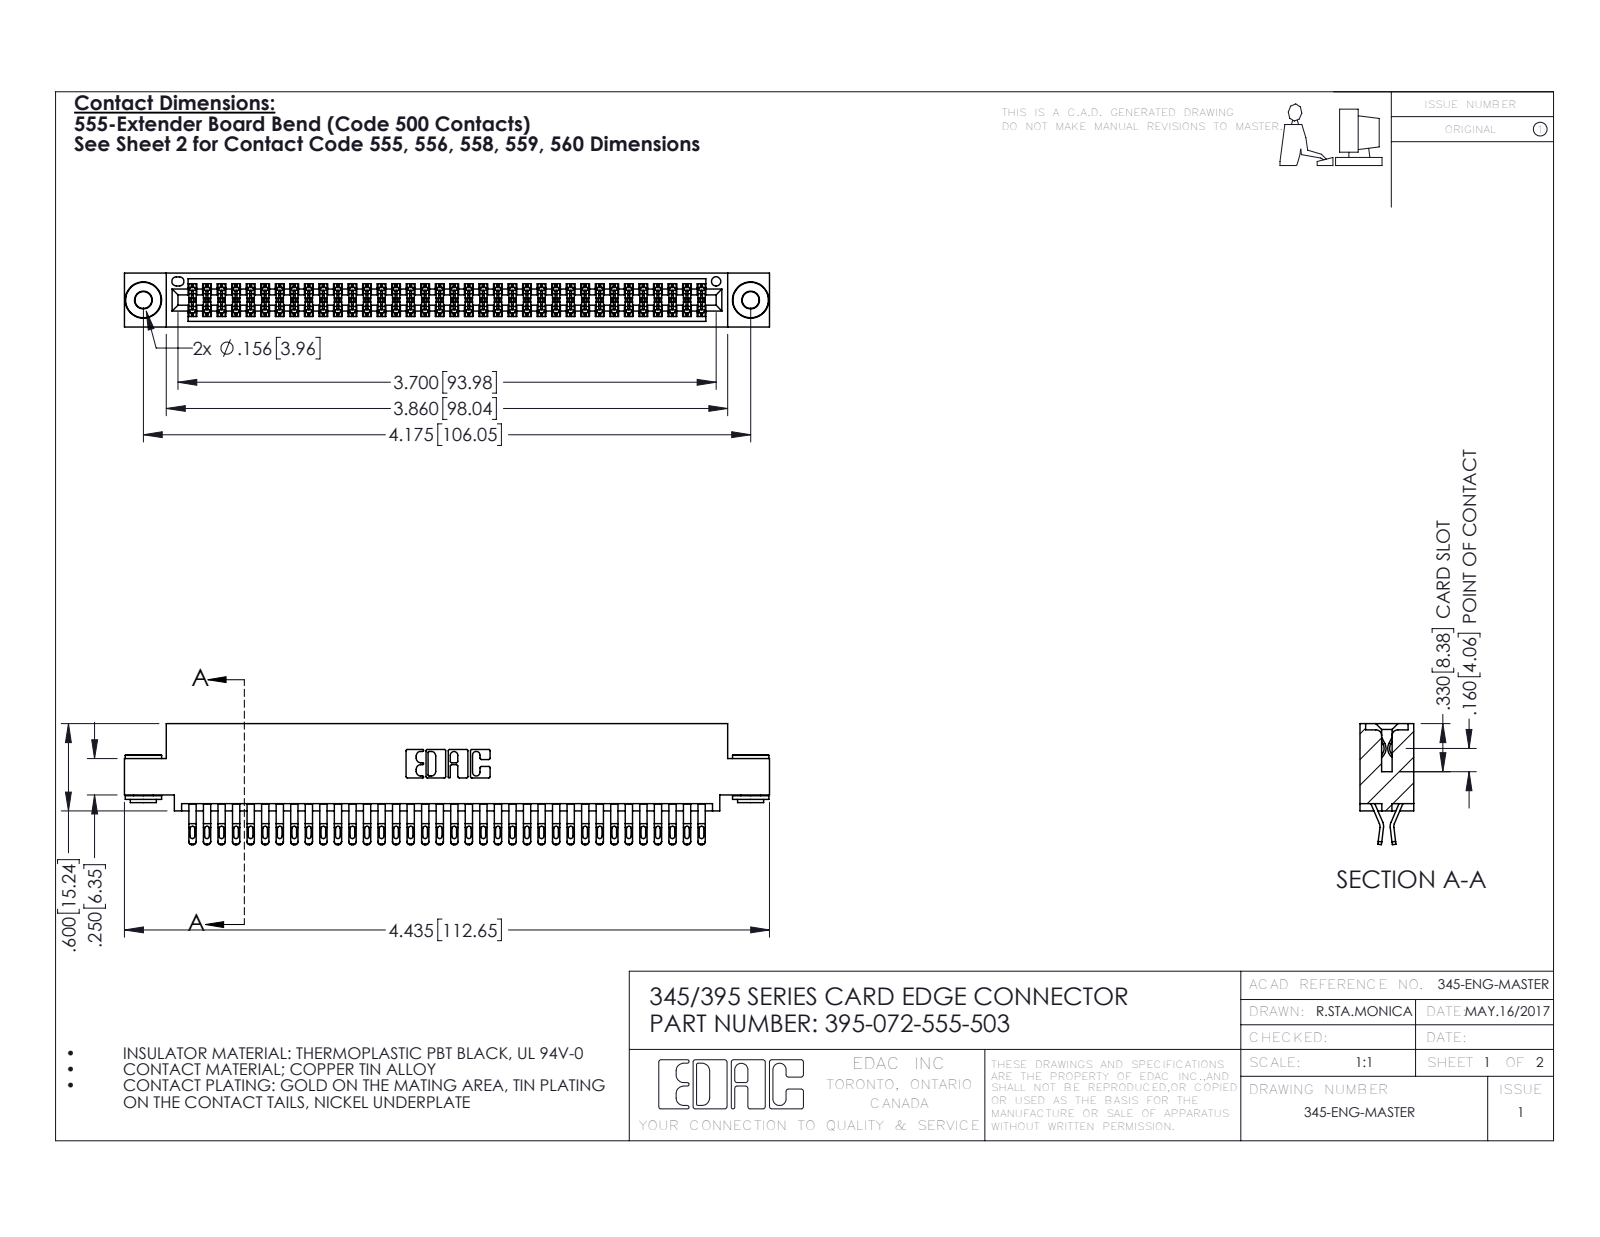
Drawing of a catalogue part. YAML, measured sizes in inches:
part_name: "395-072-555-503; 345-250-002_345-250-002-102; 345-292-001_555 Tail; 345 Part_0.110 Offset - 0.156 Dia-TH"
step_written_by: "SolidWorks 2016 (CONFIG_CONTROL_DESIGN)"
units: inches
bodies: {solids: 75, faces: 4200, planar: 2326, cylindrical: 1866, other: 8}
overall_size: [4.435, 0.832, 0.37]
volume: 0.674
surface_area: 26.71
round_holes:
  - {diameter: 0.116, count: 2}
  - {diameter: 0.156, count: 2}
  - {diameter: 0.064, count: 1}
round_bosses_or_shafts:
  - {diameter: 0.25, count: 2}
  - {diameter: 0.18, count: 2}
  - {diameter: 0.136, count: 2}
partial_cylinders:
  - {radius: 0.016, count: 180}
  - {radius: 0.02, count: 144}
  - {radius: 0.006, count: 108}
  - {radius: 0.01, count: 22}
  - {radius: 0.007, count: 6}
  - {radius: 0.031, count: 6}
  - {radius: 0.026, count: 3}
  - {radius: 0.01, count: 2}
face_to_face_distances: [0.072, 0.298, 0.025, 0.37, 0.2, 0.098, 0.272, 0.225, 0.175, 0.149]
hole_center_spacings: [0.27, 3.939, 4.175]
